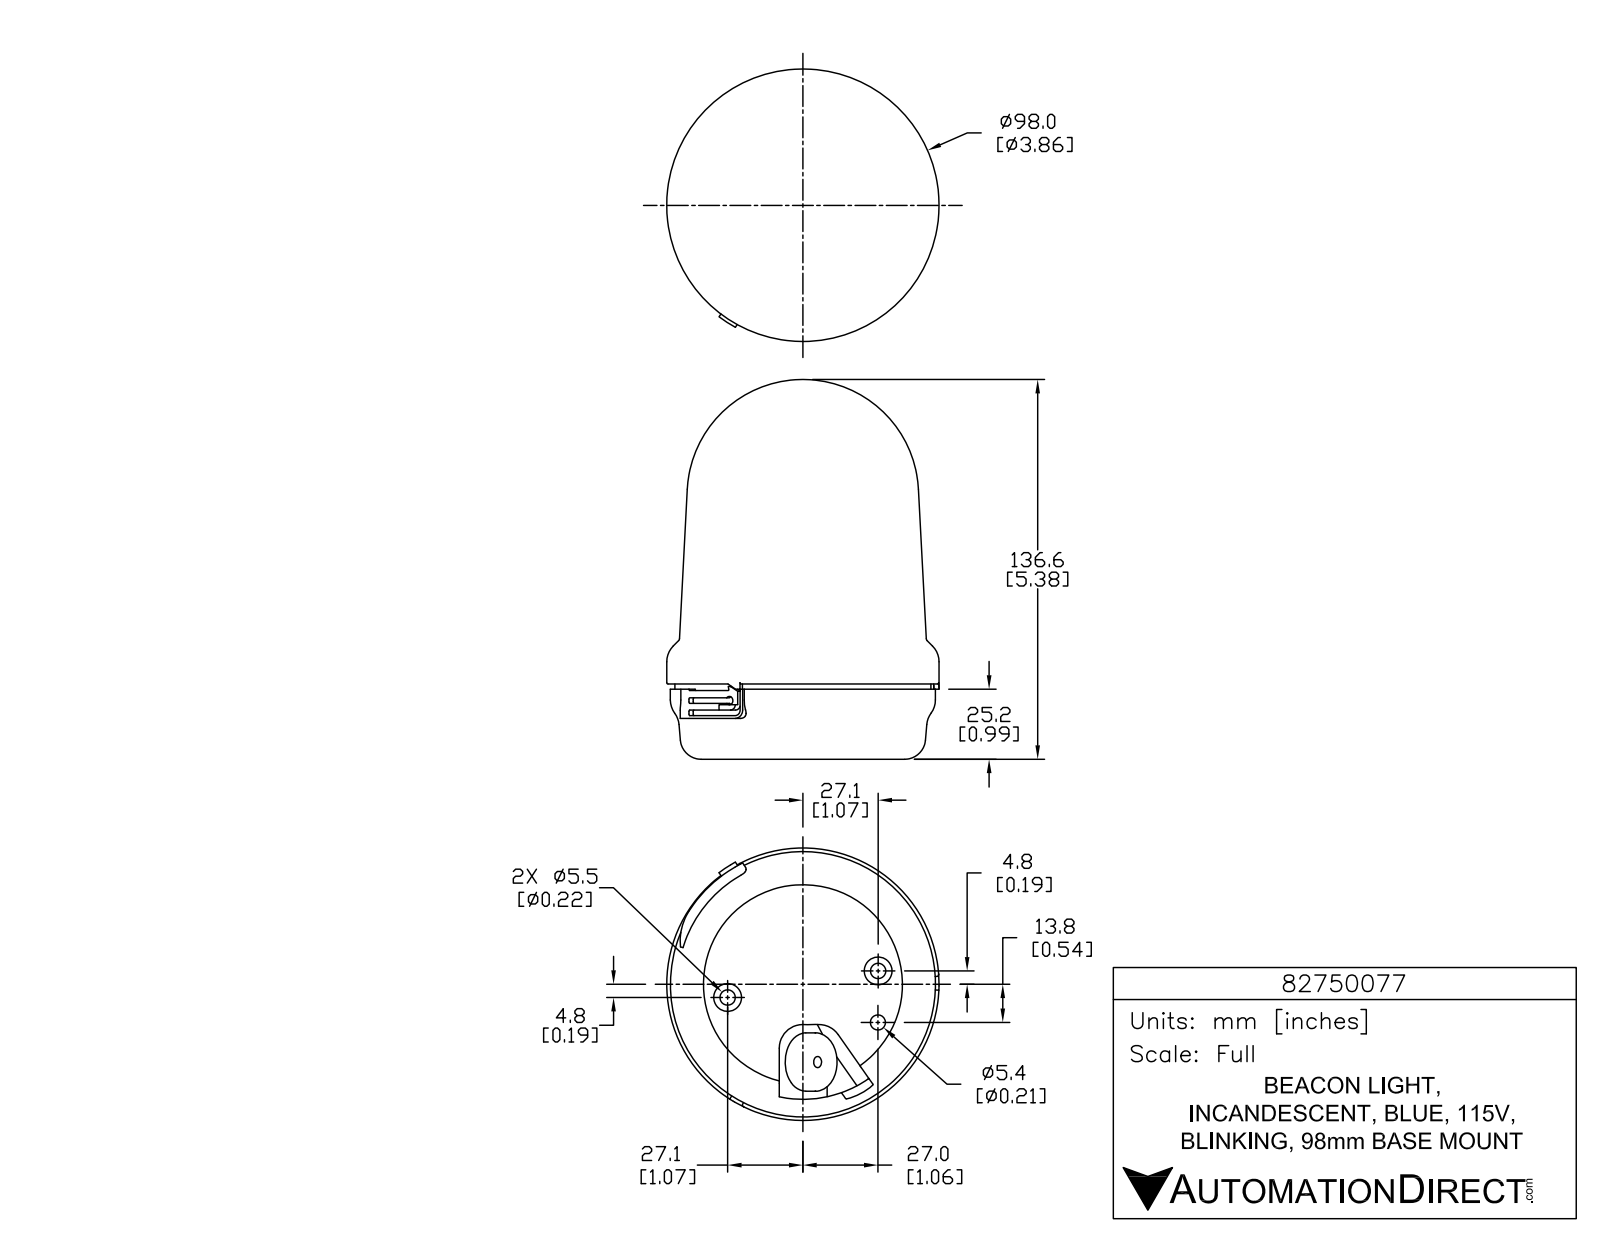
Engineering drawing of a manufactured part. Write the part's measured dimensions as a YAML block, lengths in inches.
part_name: "82750077"
step_written_by: "SolidWorks 2015 (AUTOMOTIVE_DESIGN)"
units: inches
bodies: {solids: 1, faces: 872, planar: 566, cylindrical: 204, other: 102}
overall_size: [5.378, 3.858, 3.858]
volume: 44.69
surface_area: 73.66
round_holes:
  - {diameter: 0.059, count: 3}
  - {diameter: 0.217, count: 2}
  - {diameter: 0.157, count: 1}
  - {diameter: 0.213, count: 1}
  - {diameter: 2.819, count: 1}
round_bosses_or_shafts:
  - {diameter: 0.339, count: 3}
  - {diameter: 0.084, count: 3}
  - {diameter: 0.394, count: 2}
  - {diameter: 3.858, count: 1}
  - {diameter: 3.756, count: 1}
  - {diameter: 3.626, count: 1}
  - {diameter: 0.827, count: 1}
partial_cylinders:
  - {radius: 0.005, count: 9}
  - {radius: 0.005, count: 6}
  - {radius: 0.012, count: 6}
  - {radius: 0.012, count: 6}
  - {radius: 0.012, count: 6}
  - {radius: 0.196, count: 6}
  - {radius: 0.02, count: 5}
  - {radius: 0.039, count: 4}
face_to_face_distances: [1.045, 0.972, 0.073, 0.02, 0.992, 1.065, 0.236, 0.579, 0.559, 0.413]
hole_center_spacings: [1.083, 0.73, 1.193, 2.158, 2.165]
